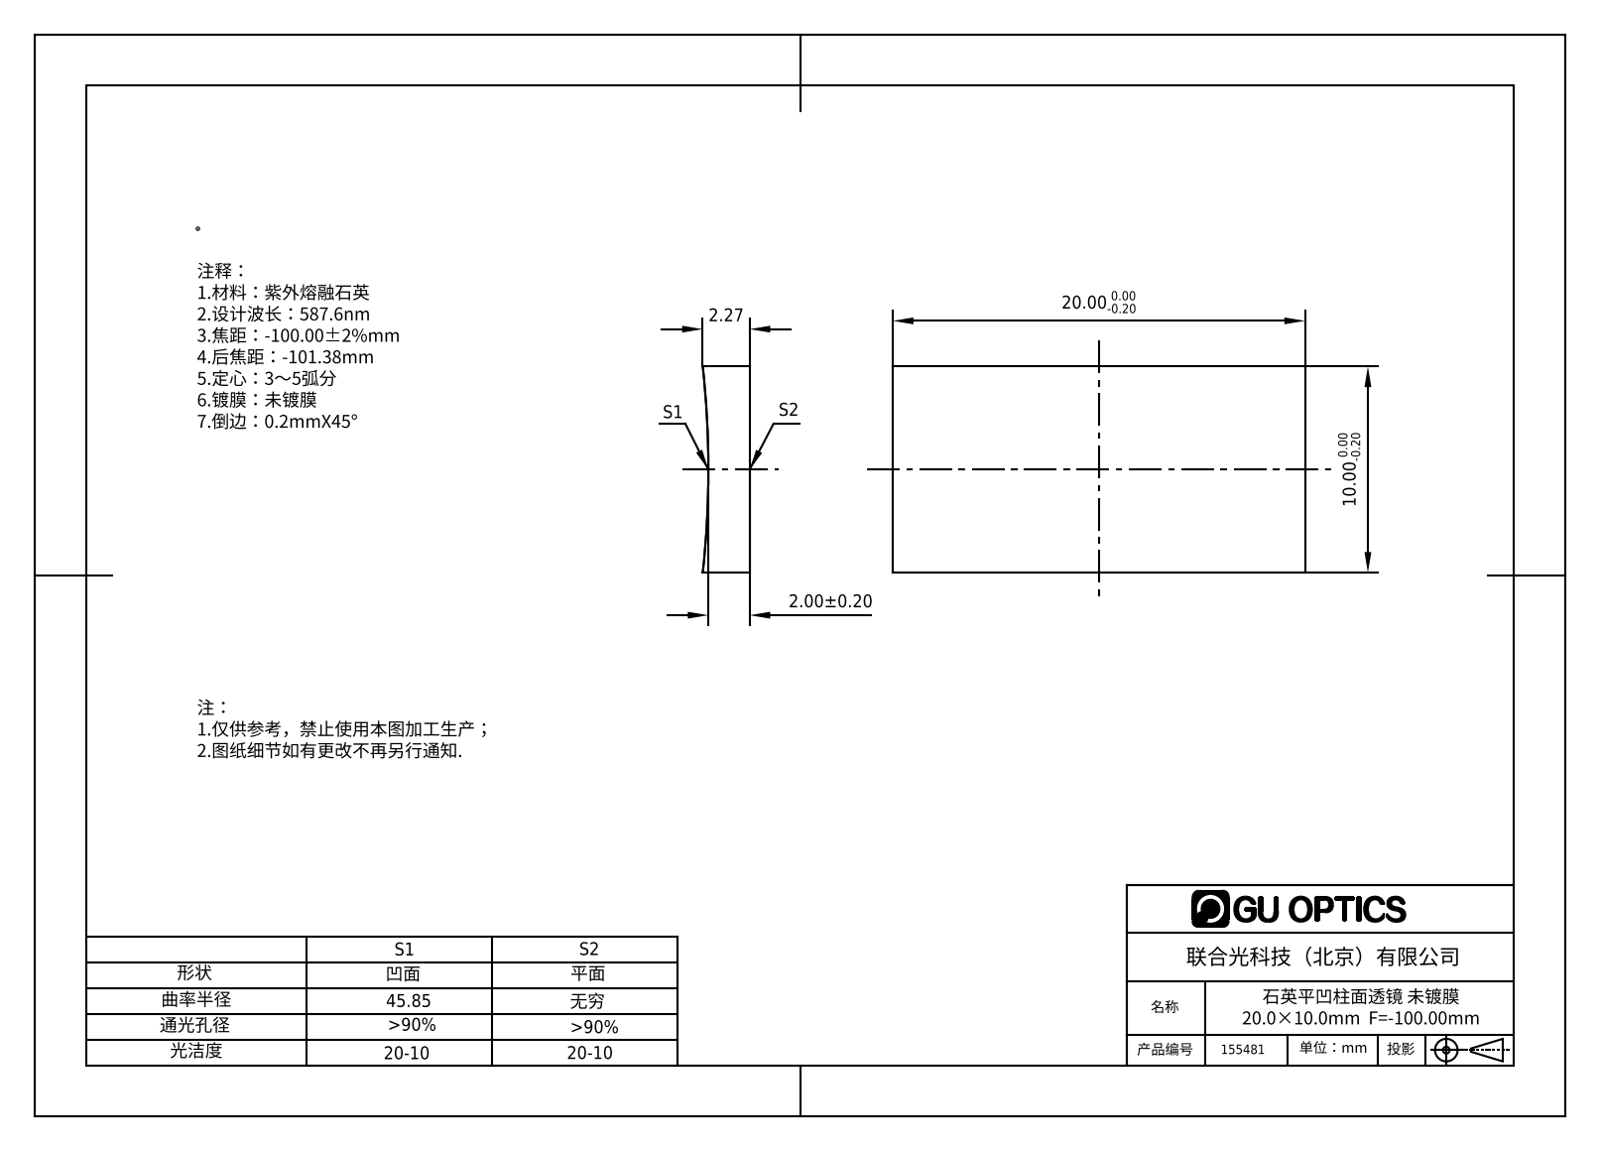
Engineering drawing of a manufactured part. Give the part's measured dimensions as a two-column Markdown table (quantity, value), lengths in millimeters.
| quantity | value |
| --- | --- |
| part name | 155481 |
| STEP written by | SolidWorks 2016 (AUTOMOTIVE_DESIGN) |
| units | millimeters |
| bodies | 1 solid, 6 faces (5 planar, 1 cylindrical, 0 other) |
| overall size | 20 × 10 × 2.27 |
| volume | 418 mm³ |
| surface area | 533 mm² |
| partial cylindrical surfaces (radius × count) | 45.85 × 1 |
| main face-to-face distances | 10, 20 |
